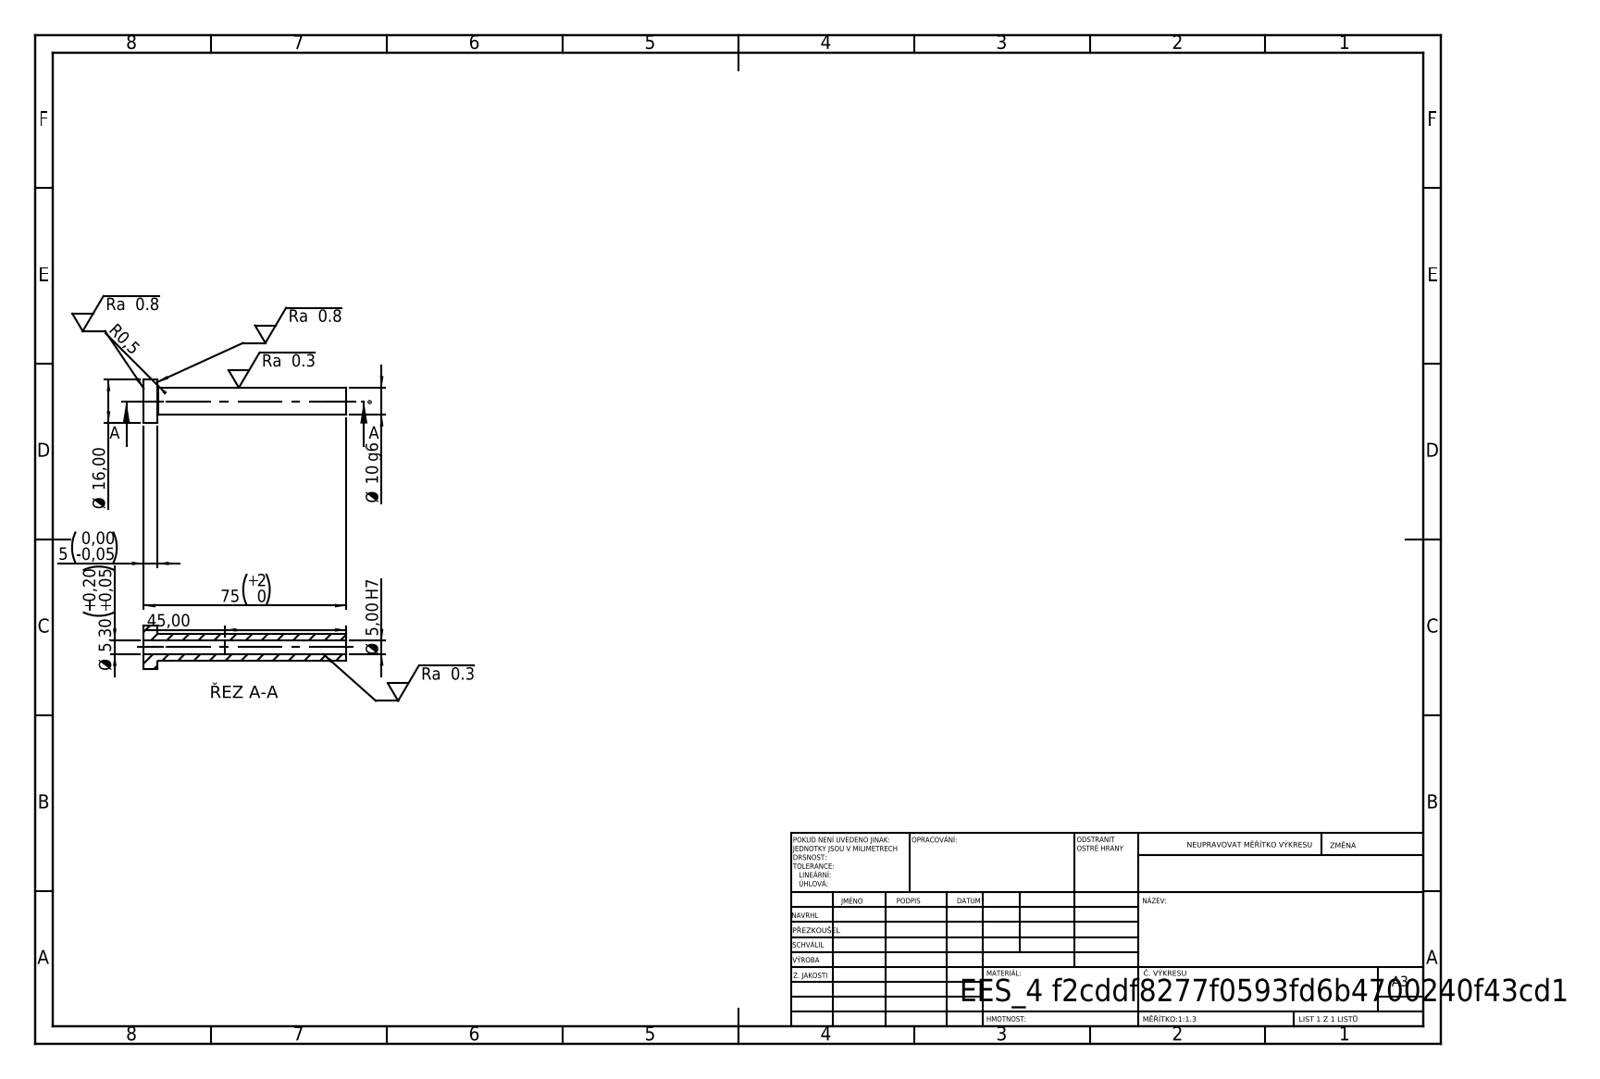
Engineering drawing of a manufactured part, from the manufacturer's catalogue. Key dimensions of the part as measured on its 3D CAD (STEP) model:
STEP written by: SolidWorks 2019 (CONFIG_CONTROL_DESIGN)
Units: millimetres
Bodies: 1 solid, 14 faces (4 planar, 8 cylindrical, 2 other)
Overall size (bounding box): 75 × 16 × 16
Volume: 4 959 mm³ · Surface area: 4 013 mm²
Round holes (diameter × count): ⌀5 ×1, ⌀5.3 ×1
Round bosses / shafts (diameter × count): ⌀16 ×1, ⌀10 ×1
Main face-to-face distances: 5, 75, 70, 30, 25, 45
